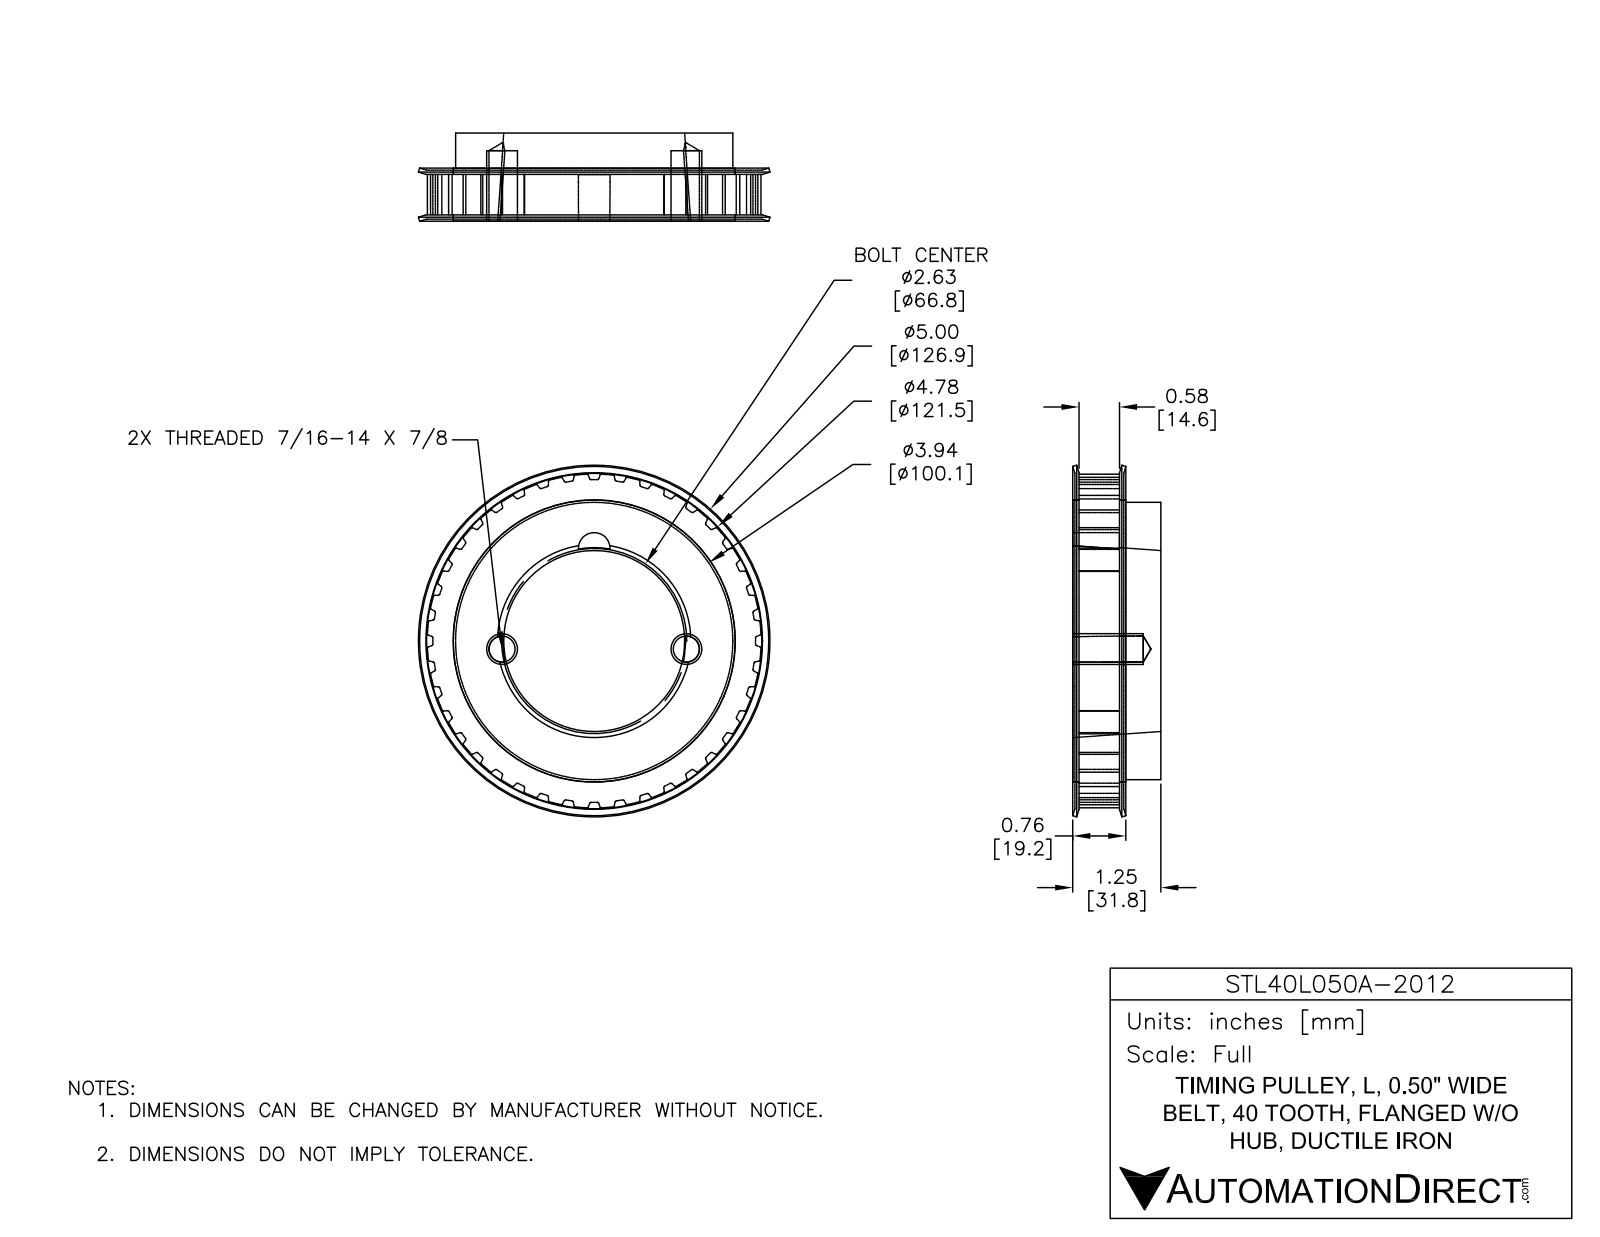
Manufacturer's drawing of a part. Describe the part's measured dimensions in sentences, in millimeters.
The part is named "STL40L050AF-2012". Its 3-D file was written by "SolidWorks 2018 (AUTOMOTIVE_DESIGN)". It is 1 solid with 388 faces: 128 planar, 242 cylindrical and 18 other. Overall it measures 126.92 by 126.92 by 31.81 millimeters. Its volume is 195 805 cubic millimeters and its surface area 40 806 square millimeters. Round bosses or shafts: 1 of diameter 101.83, 1 of diameter 100.08. Partial cylindrical surfaces (rounded edges, fillets, slot ends): 80 of radius 0.38, 80 of radius 0.51, 2 of radius 4.7, 1 of radius 5.71, 1 of radius 60.26, 1 of radius 60.26. The main face-to-face distances are 31.75, 18.35, 0.7, 13.4, 31.05, 17.65, 29.52, 16.12, 1.53, 2.23.
